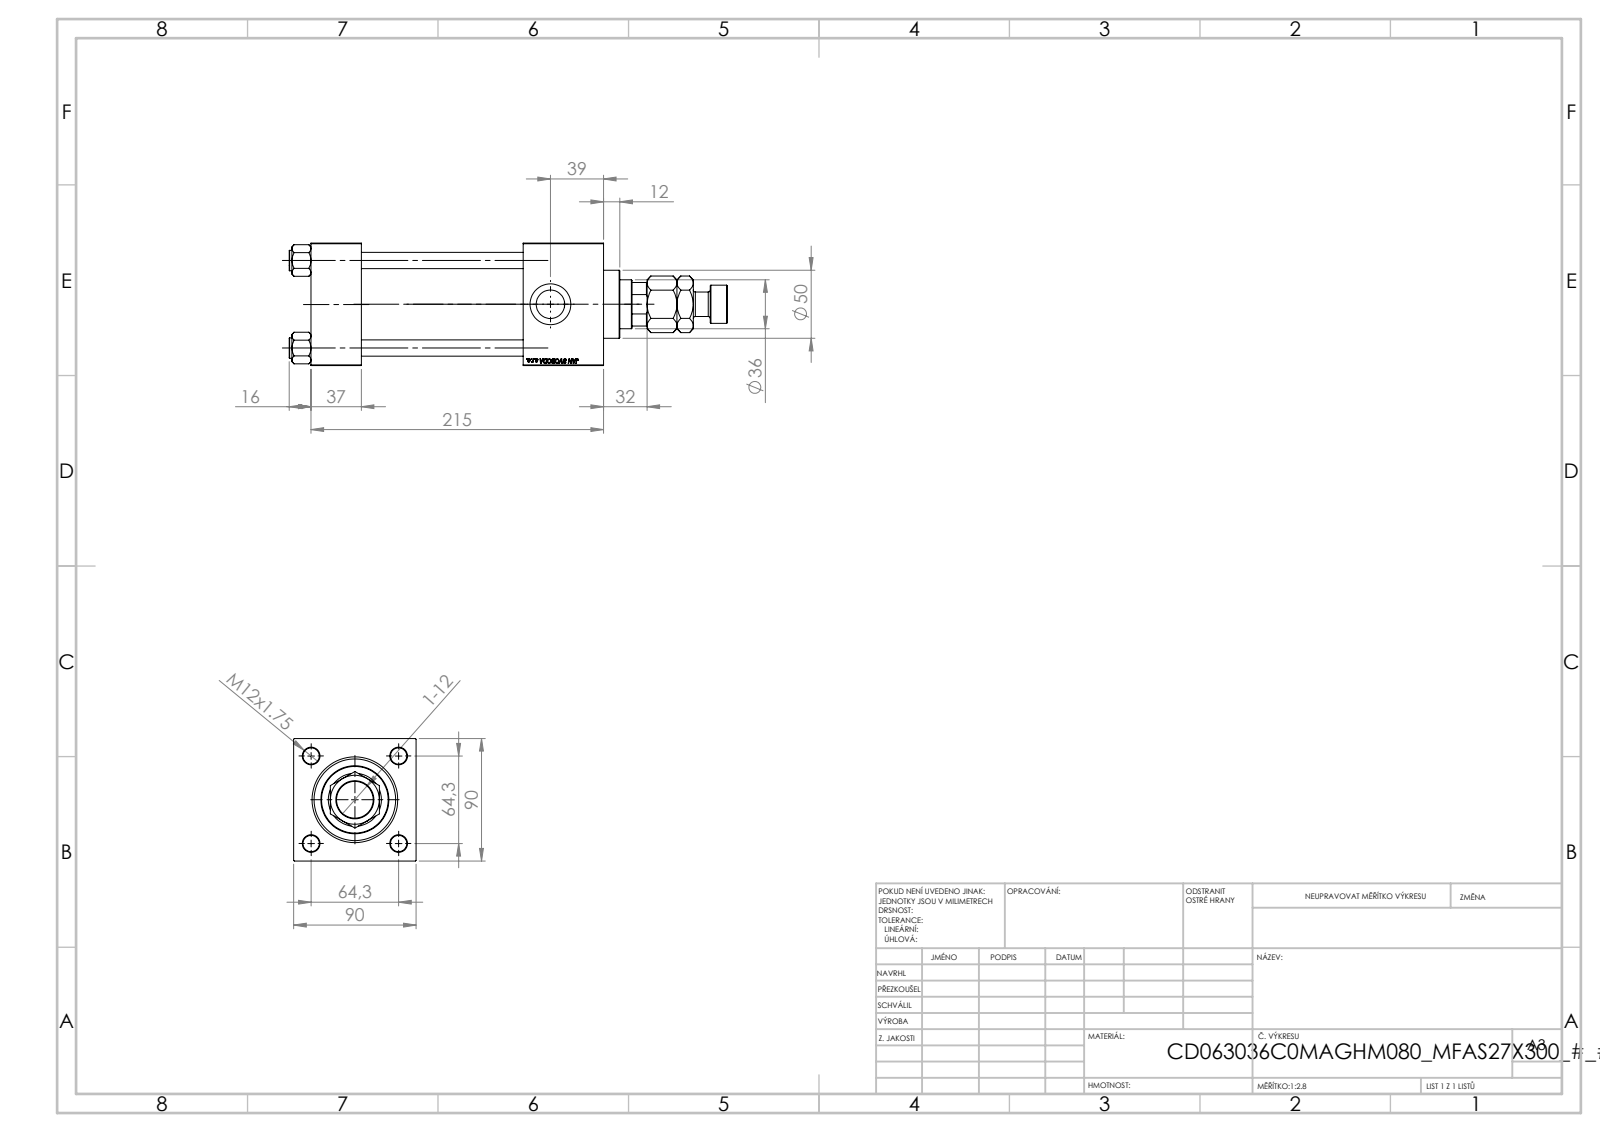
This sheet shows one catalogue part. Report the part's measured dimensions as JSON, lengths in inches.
{"part_name": "V215CD_VCP_C; MFA; V215CD_Body_C; NUT_M5_V215CD_C (+2 more)", "step_written_by": "SolidWorks 2019 (CONFIG_CONTROL_DESIGN)", "units": "inches", "bodies": {"solids": 12, "faces": 1201, "planar": 542, "cylindrical": 91, "other": 568}, "overall_size": [12.677, 3.543, 3.543], "volume_in3": 69.69, "surface_area_in2": 362.3, "round_holes": [[0.472, 4], [0.276, 2], [0.825, 2], [1.181, 2], [1.004, 1], [1.417, 1], [1.535, 1], [1.969, 1], [2.362, 1], [2.48, 1]], "round_bosses_or_shafts": [[0.591, 4], [2.717, 1], [1.102, 1], [0.709, 1]], "partial_cylinders_radius": [[0.689, 1]], "face_to_face_distances": [3.543, 1.457, 2.323, 8.465, 7.008, 6.142, 4.685, 7.335, 5.878, 1.193], "hole_center_spacings": [1.79, 2.531, 3.58]}
